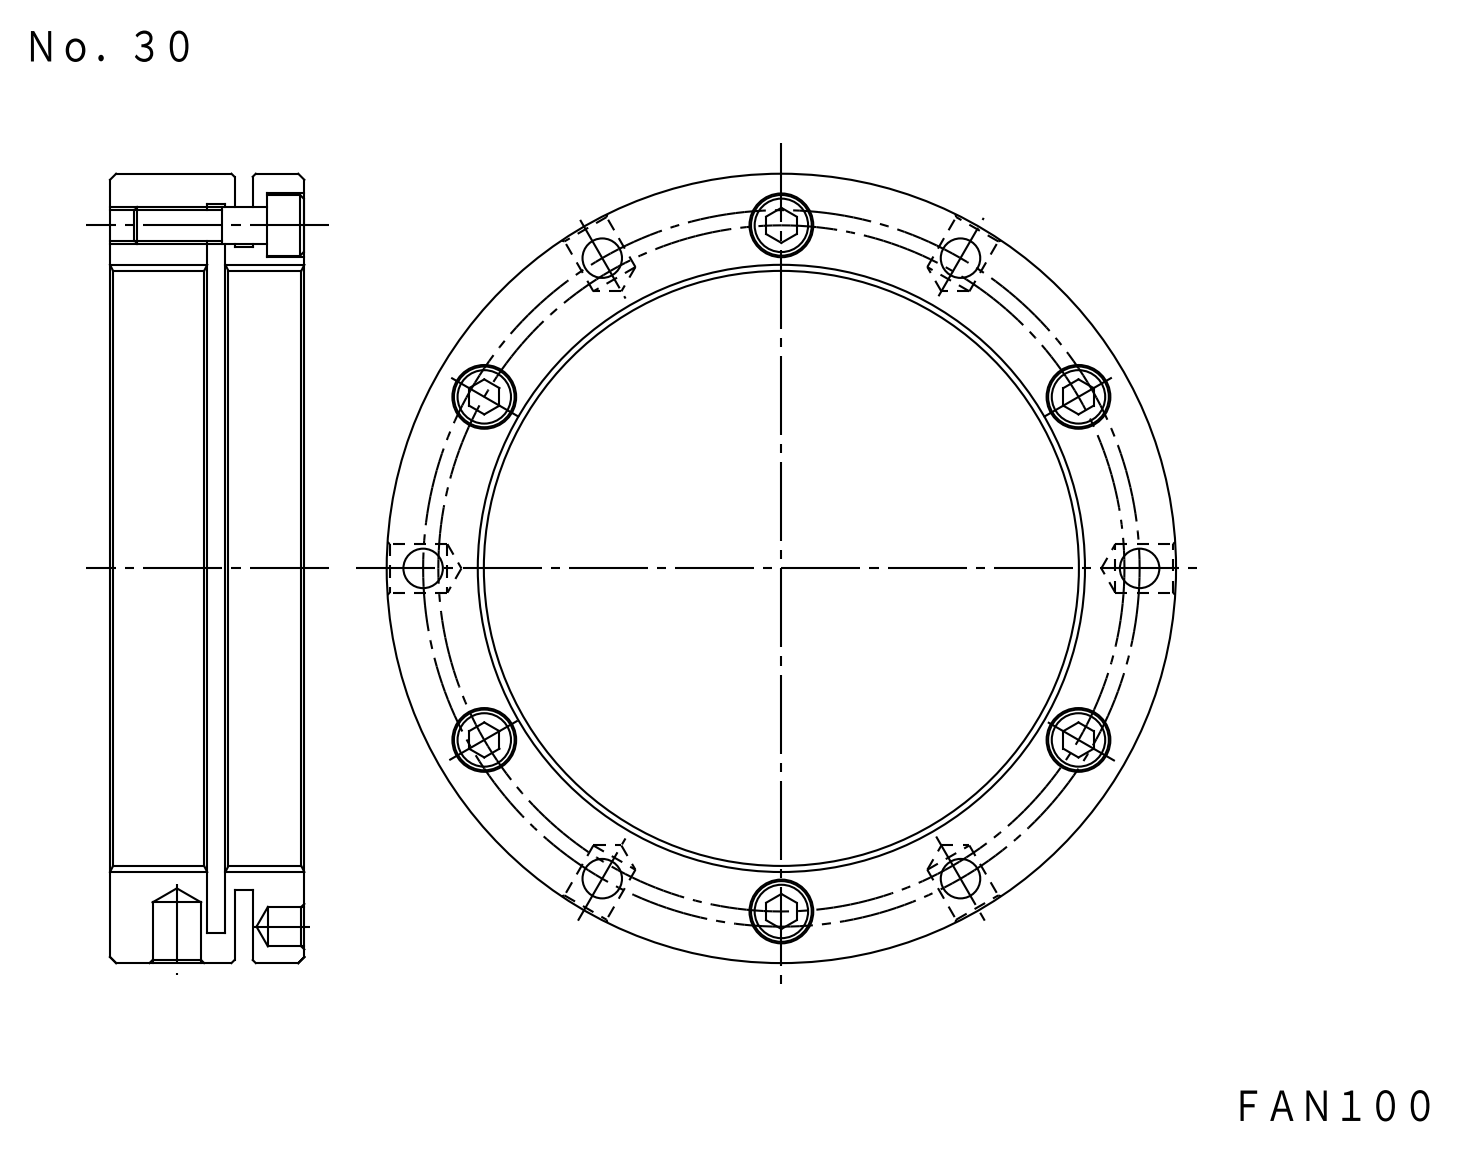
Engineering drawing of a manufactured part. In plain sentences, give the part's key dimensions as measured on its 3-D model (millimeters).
The part is named "FKD FAN100; M6X22_default". Its 3-D file was written by "SolidWorks 2012 (CONFIG_CONTROL_DESIGN)". It is 7 solids with 204 faces: 72 planar, 108 cylindrical and 24 other. Overall it measures 130 by 130 by 32 millimeters. Its volume is 149 986 cubic millimeters and its surface area 58 958 square millimeters. Round holes: 6 of diameter 6.3, 6 of diameter 6.5, 6 of diameter 10.5, 4 of diameter 4.92, 3 of diameter 8, 2 of diameter 4.92, 1 of diameter 100, 1 of diameter 123. Round bosses or shafts: 6 of diameter 10, 6 of diameter 6, 1 of diameter 130, 1 of diameter 109. The main face-to-face distances are 2.5, 4, 32, 17, 15, 19.5, 12.5, 21, 1.5, 11. The hole center spacings are 30.3, 58, 59, 82.74, 113.02, 100.46, 82.73, 102.19.
